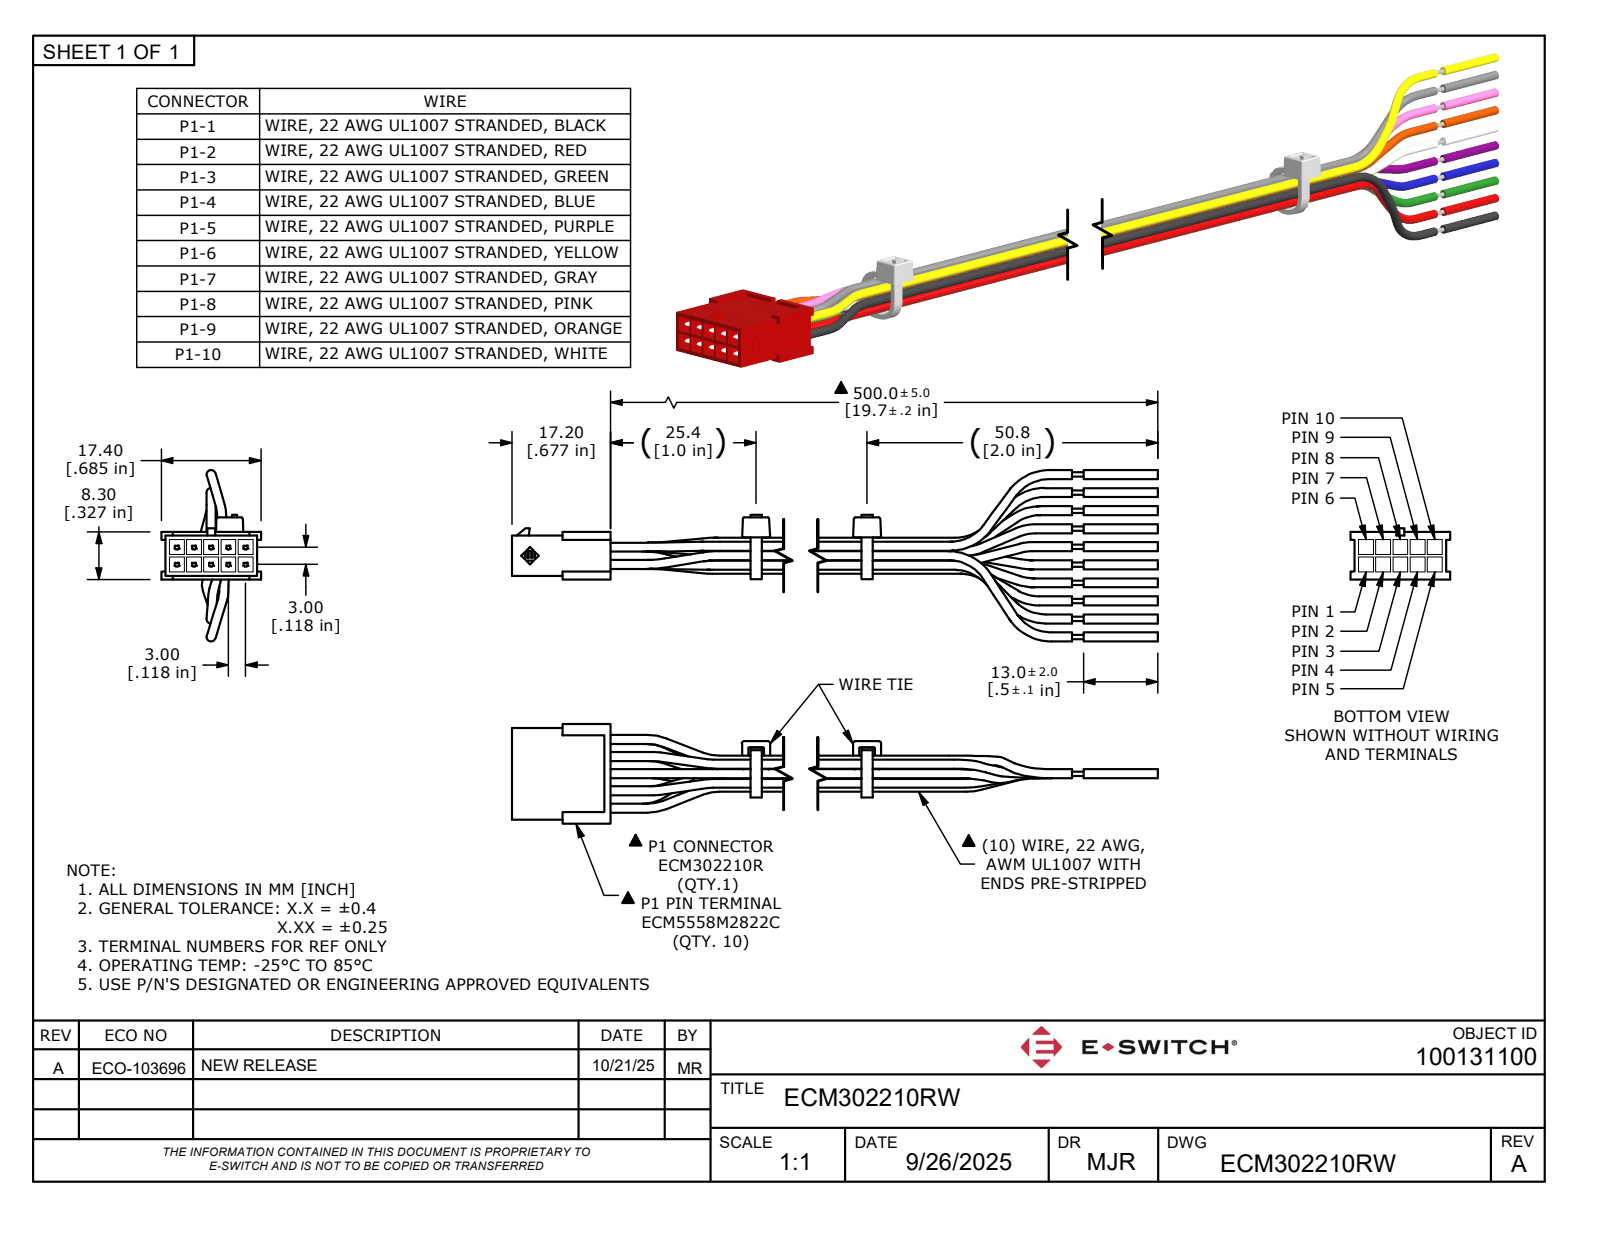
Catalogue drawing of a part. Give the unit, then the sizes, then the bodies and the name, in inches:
Units: inches
Overall size (bounding box): 20.362 × 1.178 × 0.685
Round bosses / shafts (diameter × count): ⌀0.062 ×54, ⌀0.03 ×10
Partial cylindrical surfaces — rounded edges, fillets, slot ends (radius × count): R0.008 ×55, R0.006 ×42, R0.008 ×40, R0.016 ×40, R0.024 ×40, R0.01 ×16, R0.02 ×15, R0.01 ×10
Main face-to-face distances: 0.118, 0.028, 0.248, 0.22, 0.236, 0.148, 0.128, 0.1, 0.12, 0.102
Volume: 0.676 in³ · Surface area: 45.32 in²
Bodies: 5 solids, 2338 faces (1219 planar, 682 cylindrical, 437 other)
Part name (STEP PRODUCT): ECM302210RW
STEP written by: Autodesk Inventor 2022 (AUTOMOTIVE_DESIGN)
